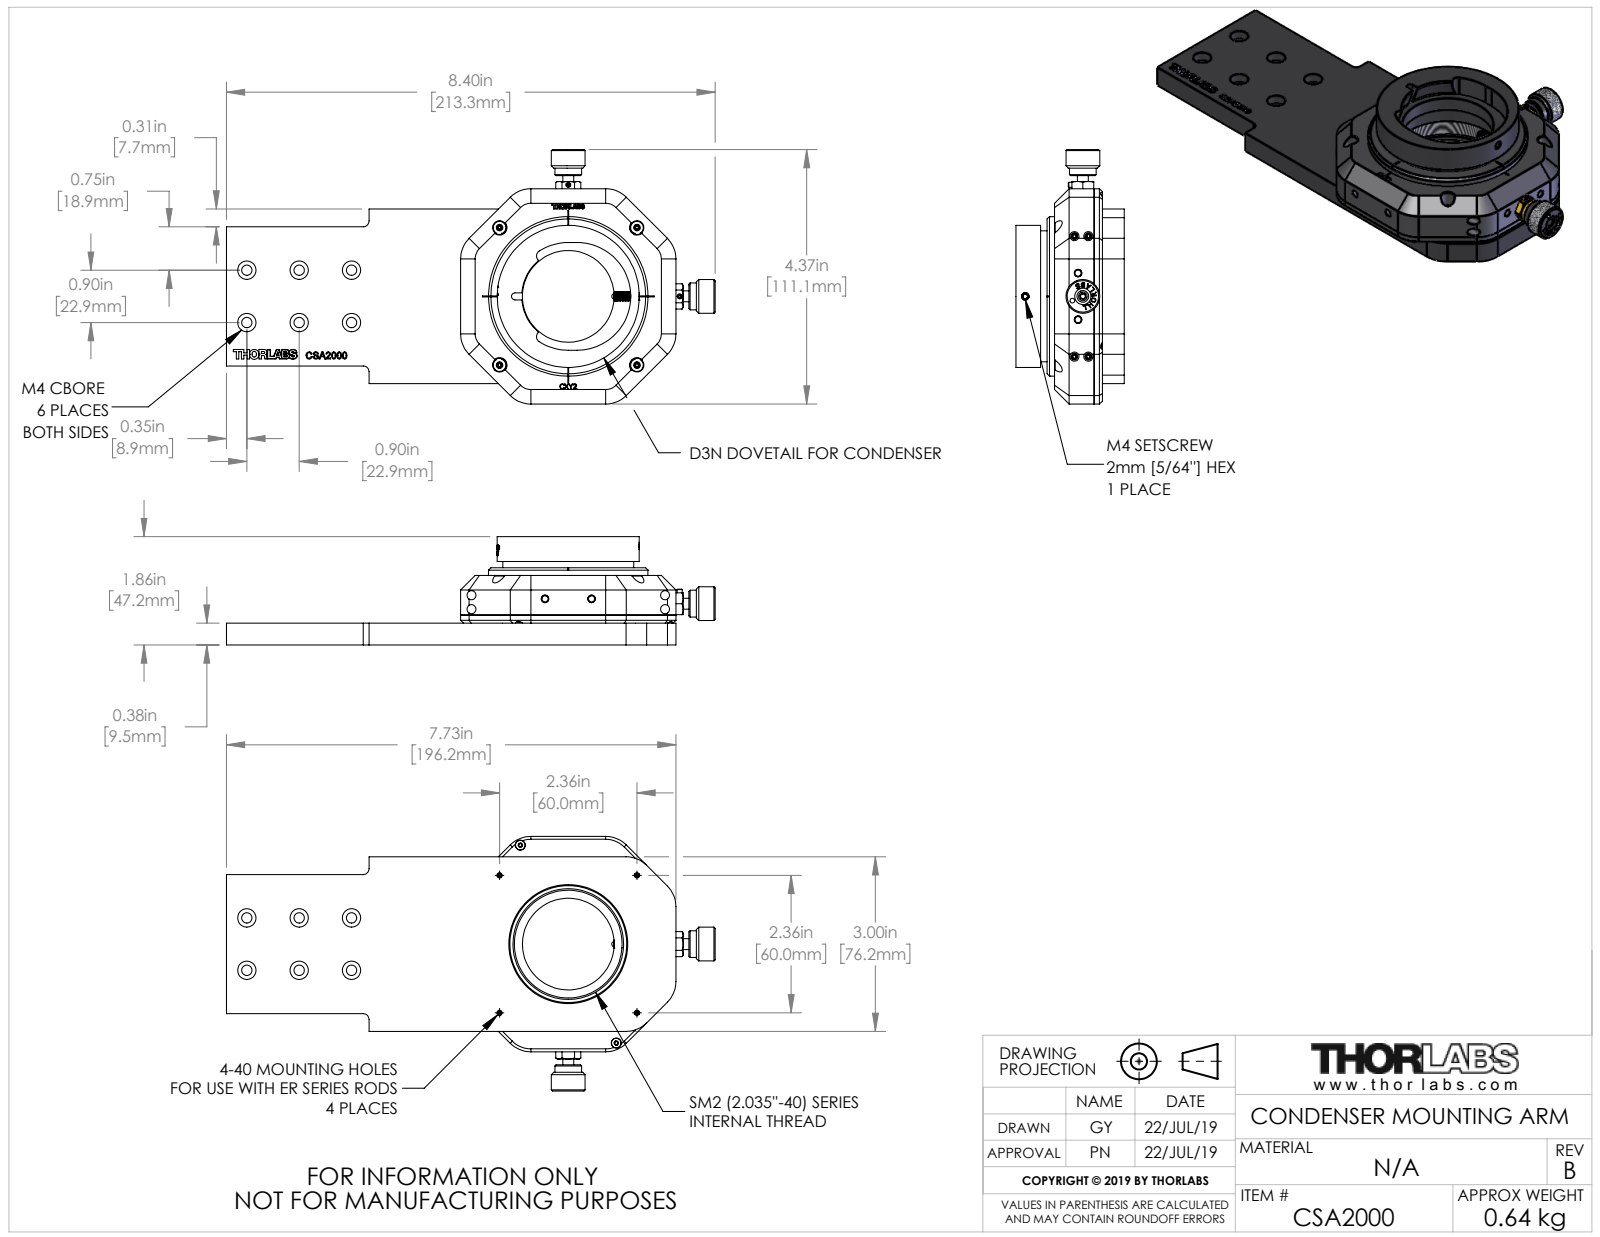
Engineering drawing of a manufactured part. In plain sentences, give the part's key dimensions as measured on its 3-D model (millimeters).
The part is named "TTN020571-E0W". Its 3-D file was written by "SolidWorks 2018 (AUTOMOTIVE_DESIGN)". It is 0 solids with 554 faces: 231 planar, 218 cylindrical and 105 other. Overall it measures 213.3 by 111.1 by 47.2 millimeters. Round holes: 6 of diameter 4.5, 6 of diameter 8, 4 of diameter 2.3, 4 of diameter 3.3, 4 of diameter 4, 4 of diameter 6, 2 of diameter 2, 2 of diameter 3.8, 2 of diameter 4.4, 2 of diameter 6, 1 of diameter 40, 1 of diameter 47. Round bosses or shafts: 2 of diameter 14.7, 2 of diameter 11.7, 2 of diameter 4.7, 2 of diameter 2.2, 1 of diameter 69.6, 1 of diameter 62, 1 of diameter 57.2, 1 of diameter 4. Partial cylindrical surfaces (rounded edges, fillets, slot ends): 10 of radius 12.7, 4 of radius 2.5, 2 of radius 23.5, 1 of radius 1.5, 1 of radius 20.3, 1 of radius 22.9, 1 of radius 31. The main face-to-face distances are 9.5, 30.4, 20.8, 3.3, 33.7, 24.1, 8.9, 13.3, 3.8, 17. The hole center spacings are 22.9, 10.4, 32.3, 6.1, 20.3, 42.4, 42.4, 45.7.
